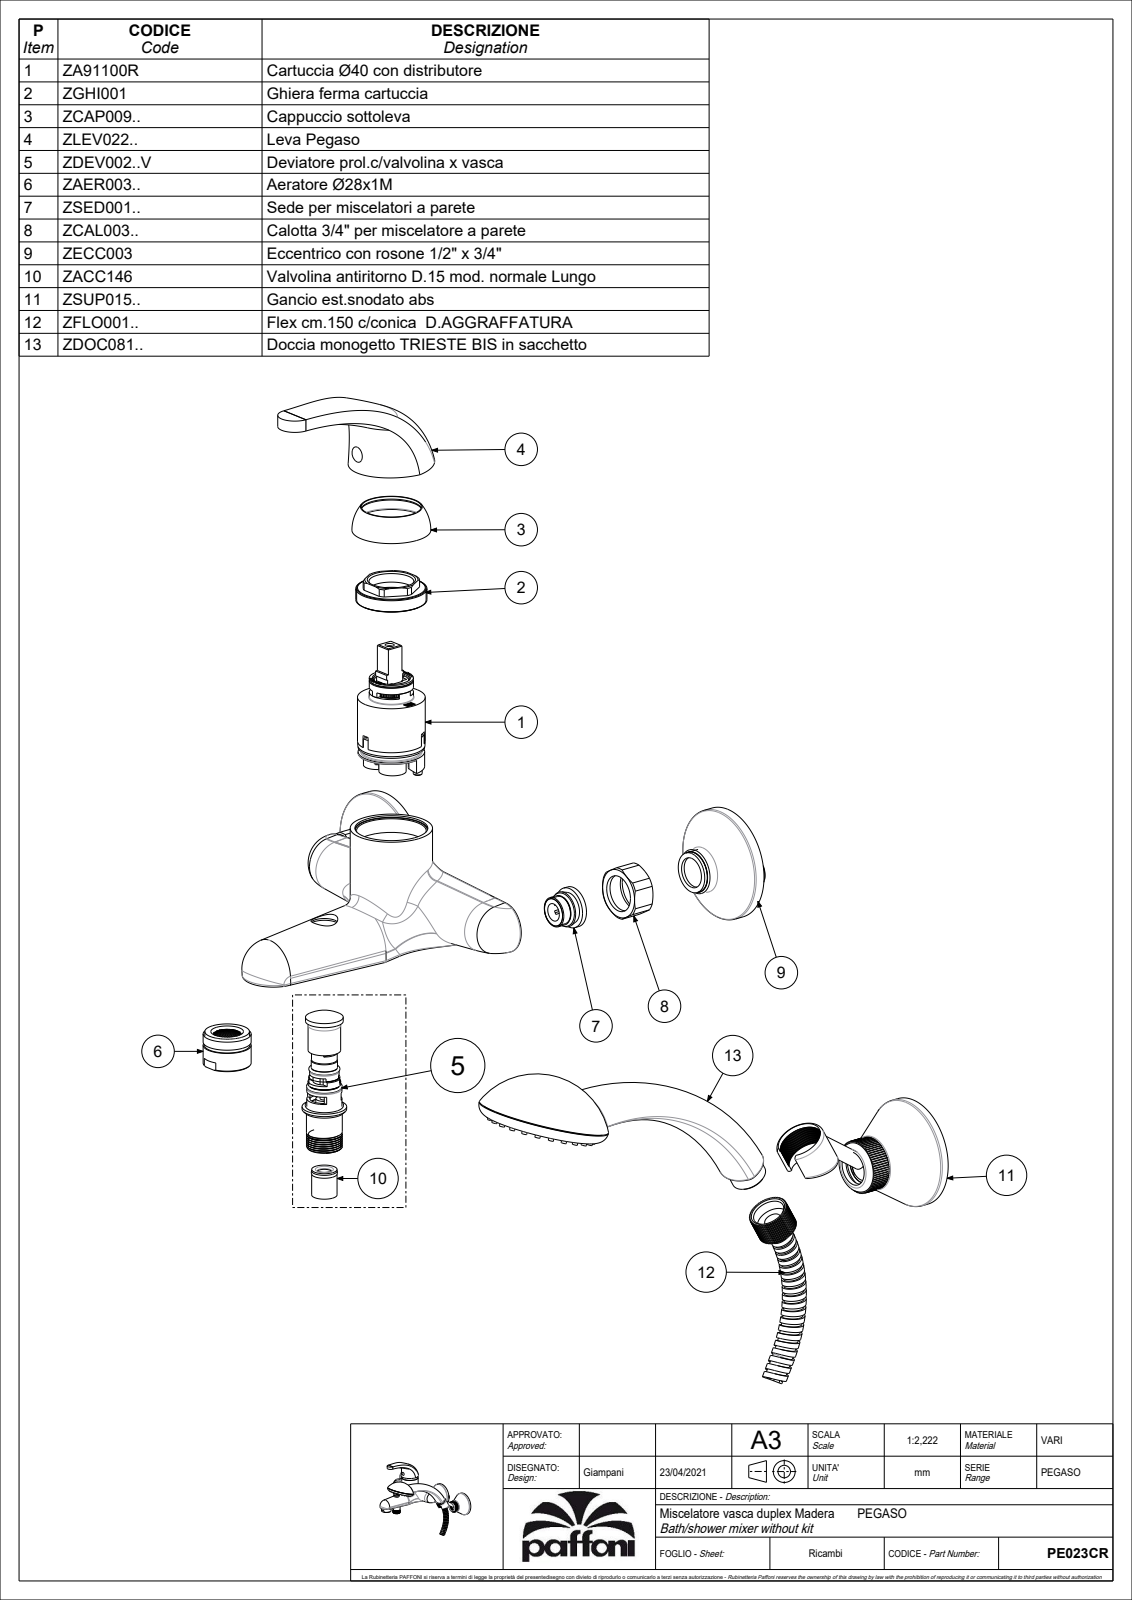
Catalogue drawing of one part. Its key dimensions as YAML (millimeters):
part_name: "PE023CR_SW0001"
step_written_by: "CREO PARAMETRIC BY PTC INC, 2022124 (CONFIG_CONTROL_DESIGN)"
units: millimeters
bodies: {solids: 6, faces: 1515, planar: 441, cylindrical: 545, other: 529}
overall_size: [323.23, 278.75, 243.95]
volume: 792202
surface_area: 151089
round_holes:
  - {diameter: 10, count: 3}
  - {diameter: 20.3, count: 2}
  - {diameter: 21.5, count: 2}
  - {diameter: 24.1, count: 2}
  - {diameter: 26.7, count: 2}
  - {diameter: 6, count: 1}
  - {diameter: 14, count: 1}
  - {diameter: 15, count: 1}
  - {diameter: 17, count: 1}
  - {diameter: 19, count: 1}
  - {diameter: 20, count: 1}
  - {diameter: 27.4, count: 1}
round_bosses_or_shafts:
  - {diameter: 66, count: 2}
  - {diameter: 26.4, count: 2}
  - {diameter: 21, count: 2}
  - {diameter: 75.5, count: 1}
  - {diameter: 64, count: 1}
  - {diameter: 48, count: 1}
  - {diameter: 29.5, count: 1}
  - {diameter: 28, count: 1}
partial_cylinders:
  - {radius: 0.25, count: 95}
  - {radius: 0.5, count: 72}
  - {radius: 1, count: 8}
  - {radius: 3.65, count: 2}
  - {radius: 3.8, count: 2}
  - {radius: 15.5, count: 2}
  - {radius: 15.89, count: 2}
  - {radius: 16.04, count: 2}
face_to_face_distances: [34, 0.5, 34.5, 29, 8, 20.5, 1.5, 33, 1, 9.5]
hole_center_spacings: [98.27, 150, 100, 186.16, 250]
